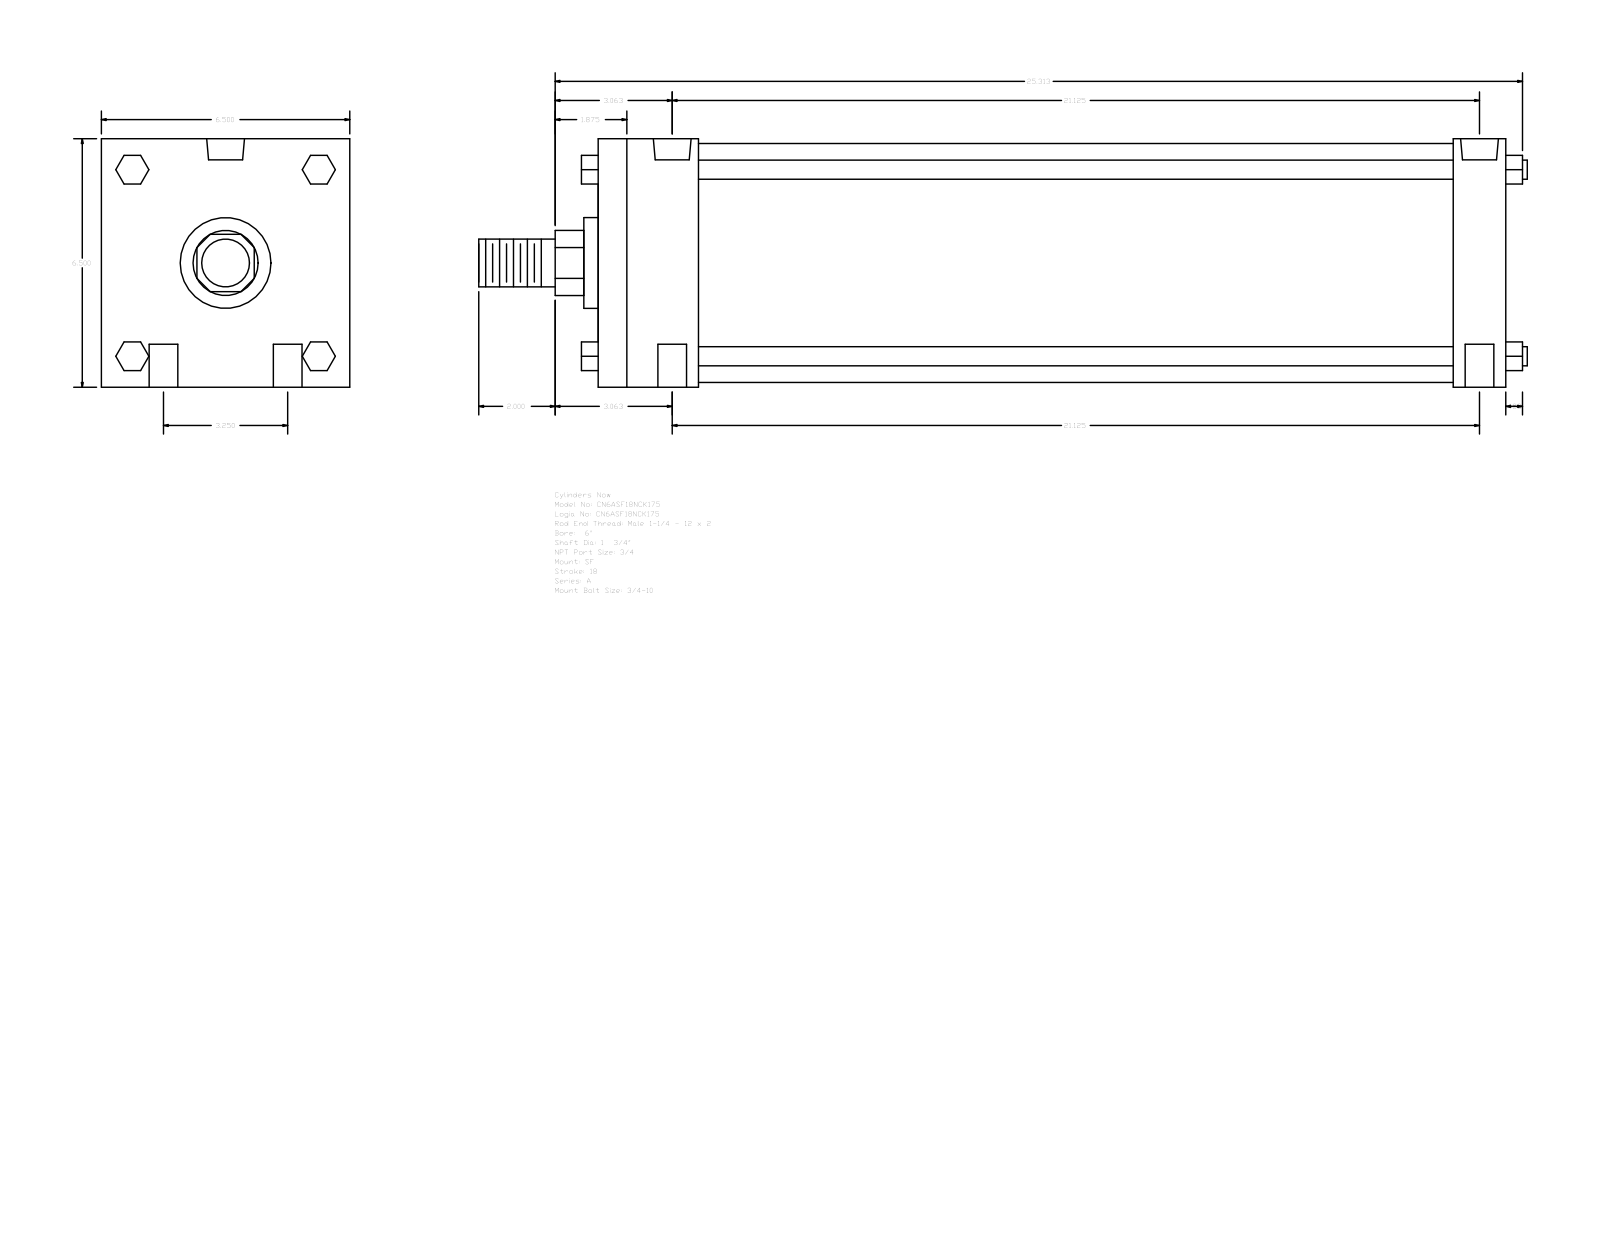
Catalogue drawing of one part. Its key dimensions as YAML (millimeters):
part_name: "A_SF__0600_1.75"
step_written_by: "GSSL Pune (CONFIG_CONTROL_DESIGN)"
units: millimeters
bodies: {solids: 0, faces: 124, planar: 94, cylindrical: 30, other: 0}
overall_size: [696.91, 165.1, 165.1]
round_holes:
  - {diameter: 19.05, count: 4}
  - {diameter: 15.08, count: 2}
  - {diameter: 25.12, count: 2}
round_bosses_or_shafts:
  - {diameter: 12.7, count: 4}
  - {diameter: 158.75, count: 1}
  - {diameter: 60.33, count: 1}
  - {diameter: 44.45, count: 1}
  - {diameter: 31.75, count: 1}
partial_cylinders:
  - {radius: 21.63, count: 1}
face_to_face_distances: [165.1, 603.26, 66.68, 568.33, 34.93, 501.65, 536.58, 19.05, 61.97, 107.34]
hole_center_spacings: [41.27, 538.15, 536.57, 82.54, 542.88, 525.45]
